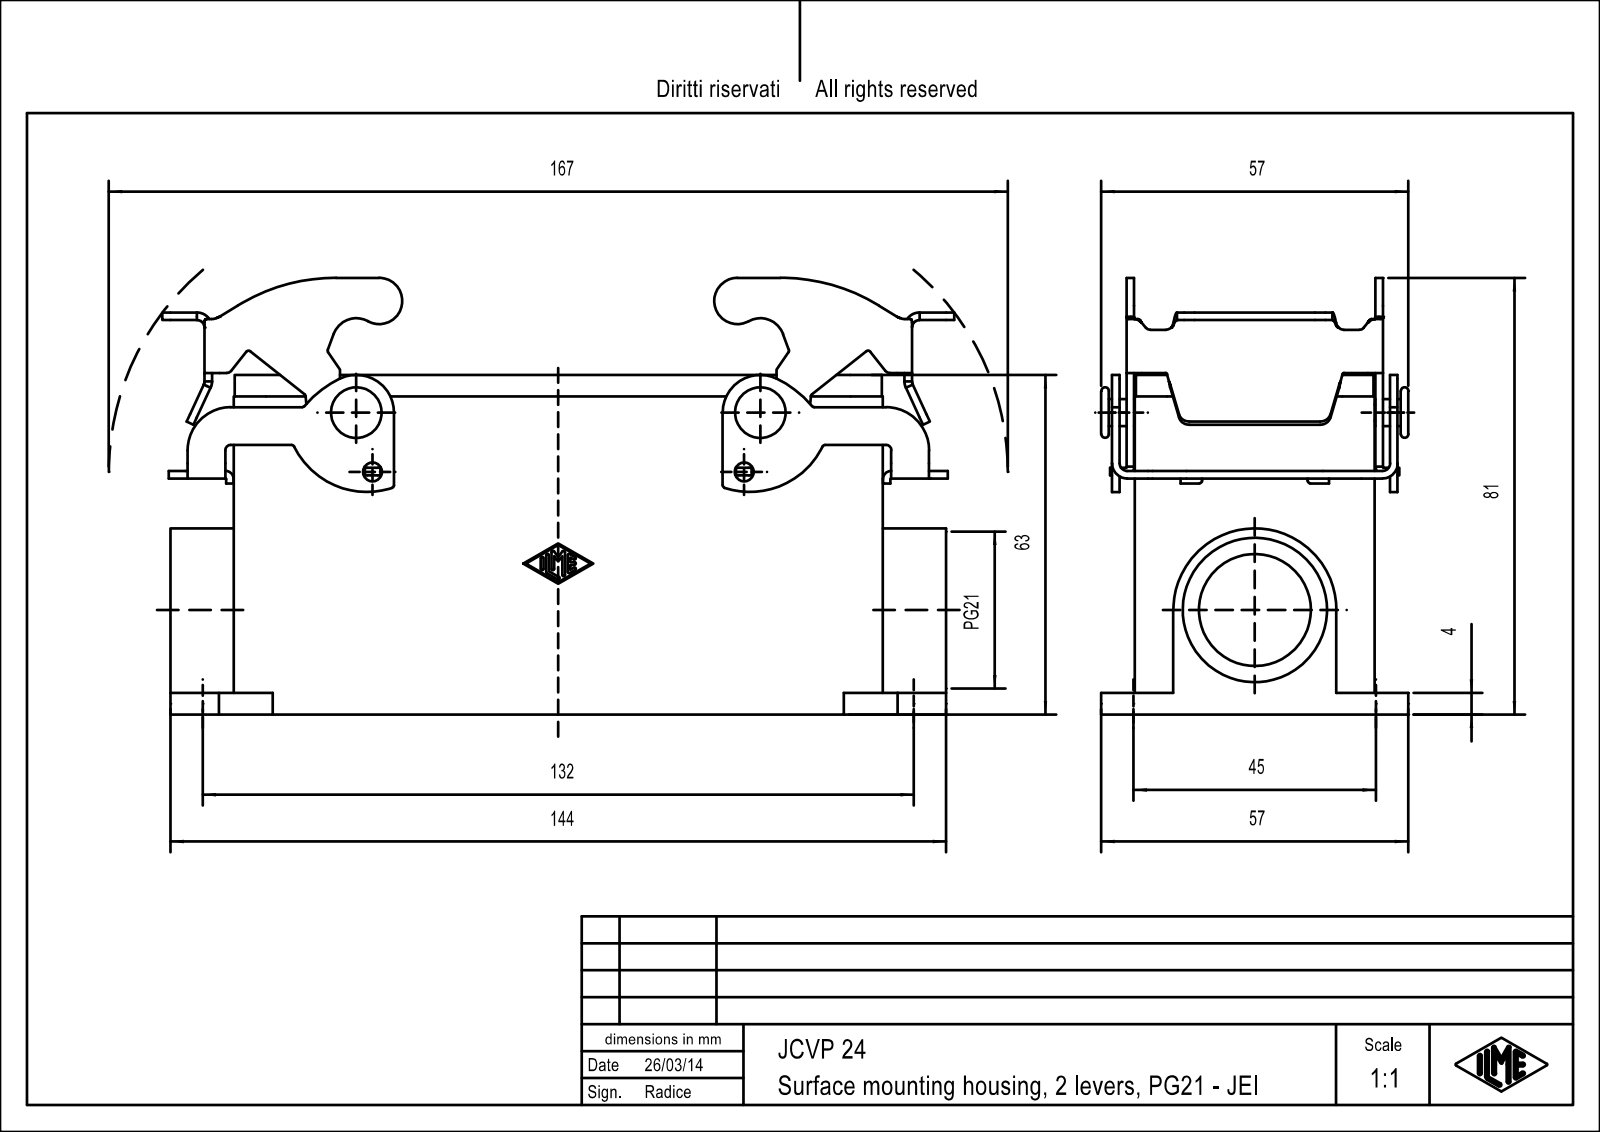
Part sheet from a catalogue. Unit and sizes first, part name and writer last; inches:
Units: inches
Overall size (bounding box): 5.786 × 3.189 × 2.244
Round holes (diameter × count): ⌀0.097 ×4, ⌀0.118 ×4, ⌀0.217 ×4, ⌀0.138 ×2, ⌀0.818 ×1, ⌀1.054 ×1
Round bosses / shafts (diameter × count): ⌀0.197 ×2, ⌀0.126 ×2, ⌀0.118 ×2
Partial cylindrical surfaces — rounded edges, fillets, slot ends (radius × count): R0.02 ×22, R0.039 ×18, R0.01 ×16, R0.059 ×14, R0.079 ×12, R0.055 ×10, R0.11 ×10, R0.315 ×6
Main face-to-face distances: 0.157, 1.594, 0.055, 1.752, 1.437, 0.106, 1.925, 0.463, 0.325, 0.163
Hole centre spacings: 0.655, 1.521, 4.659, 4.857, 1.063, 1.772, 4.094, 4.23
Volume: 7.91 in³ · Surface area: 111.2 in²
Bodies: 3 solids, 613 faces (293 planar, 272 cylindrical, 48 other)
Part name (STEP PRODUCT): p1; p2; p3; JCVP_24
STEP written by: Creo Elements/Direct Modeling 18.0B 02-Dec-2011 (C) Parametric Technology GmbH (AUTOMOTIVE_DESIGN)
